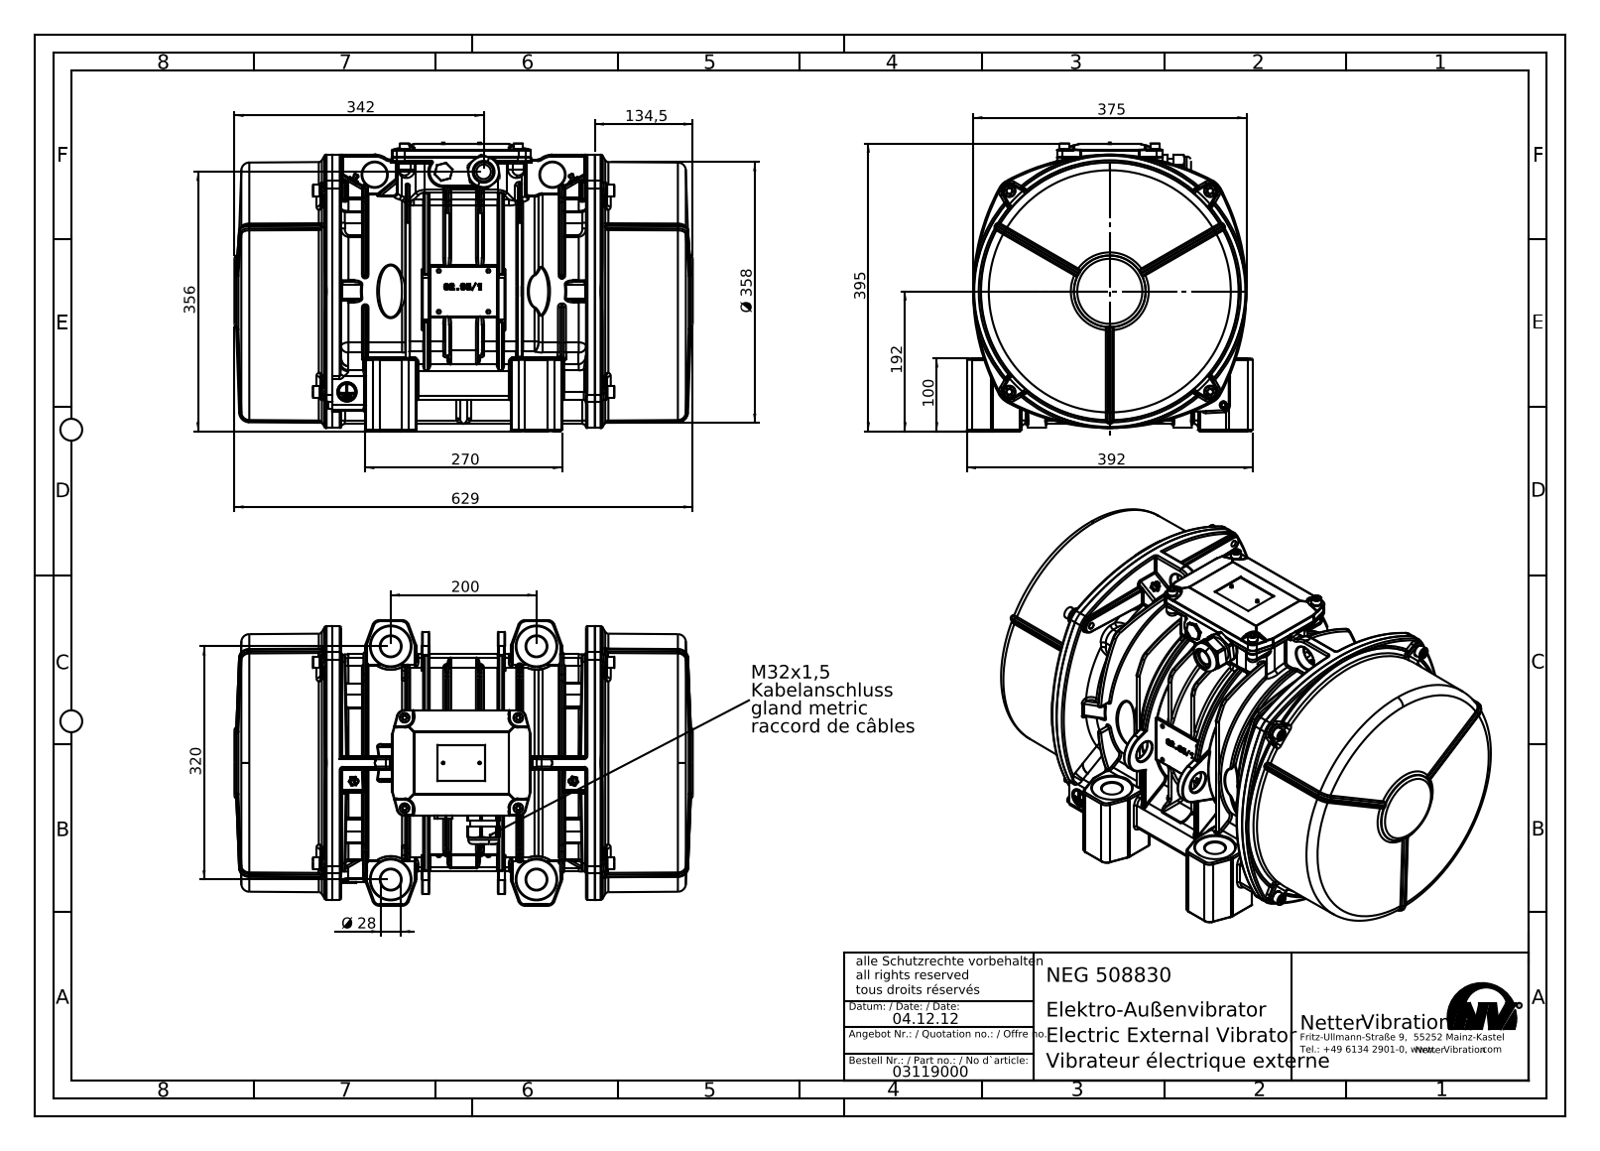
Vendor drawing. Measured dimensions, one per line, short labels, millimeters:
name: NEG 508830
written by: SolidWorks 2010 (AUTOMOTIVE_DESIGN)
unit: mm
bodies: 3 solids, 1520 faces (451 planar, 448 cylindrical, 621 other)
size: 636.4 × 395 × 392
volume: 35 750 000 mm³; area: 1 965 000 mm²
holes: 4× ⌀6.8, 4× ⌀28, 2× ⌀35, 1× ⌀12, 1× ⌀335
bosses: 8× ⌀13, 4× ⌀55, 4× ⌀8, 1× ⌀352, 1× ⌀95, 1× ⌀32.5
rounds: 86× R3, 32× R2, 30× R1, 24× R10, 8× R5, 6× R20, 4× R2.5, 4× R10.5
face distances: 360, 12, 348, 336, 45, 35, 70, 245, 33, 115
hole spacings: 190, 268.7, 200, 320, 377.36, 380, 290
